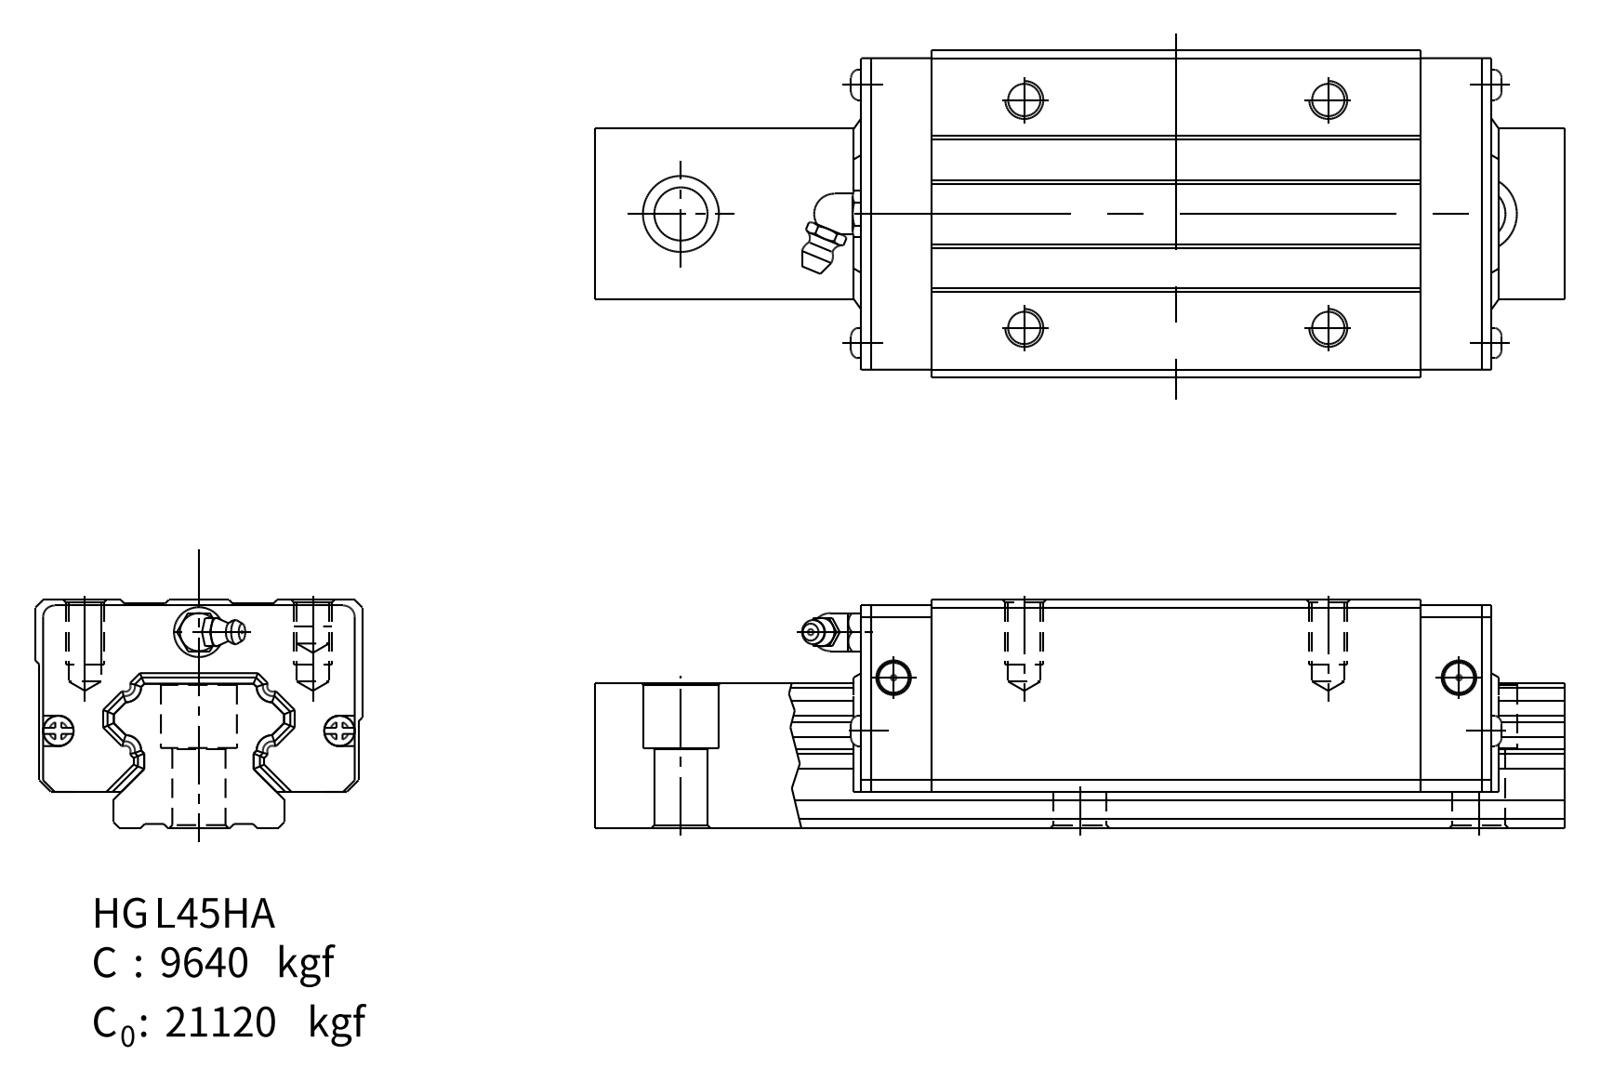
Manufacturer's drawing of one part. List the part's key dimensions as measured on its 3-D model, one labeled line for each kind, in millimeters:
Part name (STEP PRODUCT): HGH45_ASM_2_ASM_Standard; HGH45H; PRT2_Standard
STEP written by: SolidWorks 2006104 (CONFIG_CONTROL_DESIGN)
Units: millimetres
Bodies: 1 solid, 337 faces (253 planar, 24 cylindrical, 60 other)
Overall size (bounding box): 171.5 × 86 × 50.5
Volume: 540 148 mm³ · Surface area: 65 182 mm²
Round holes (diameter × count): ⌀10 ×4
Partial cylindrical surfaces — rounded edges, fillets, slot ends (radius × count): R0.8 ×4, R1.2 ×4, R4 ×4, R3 ×2
Main face-to-face distances: 1, 50.5, 28.5, 85, 22, 171.2, 49.5, 21, 49.06, 20.56
Hole centre spacings: 60, 80, 100
